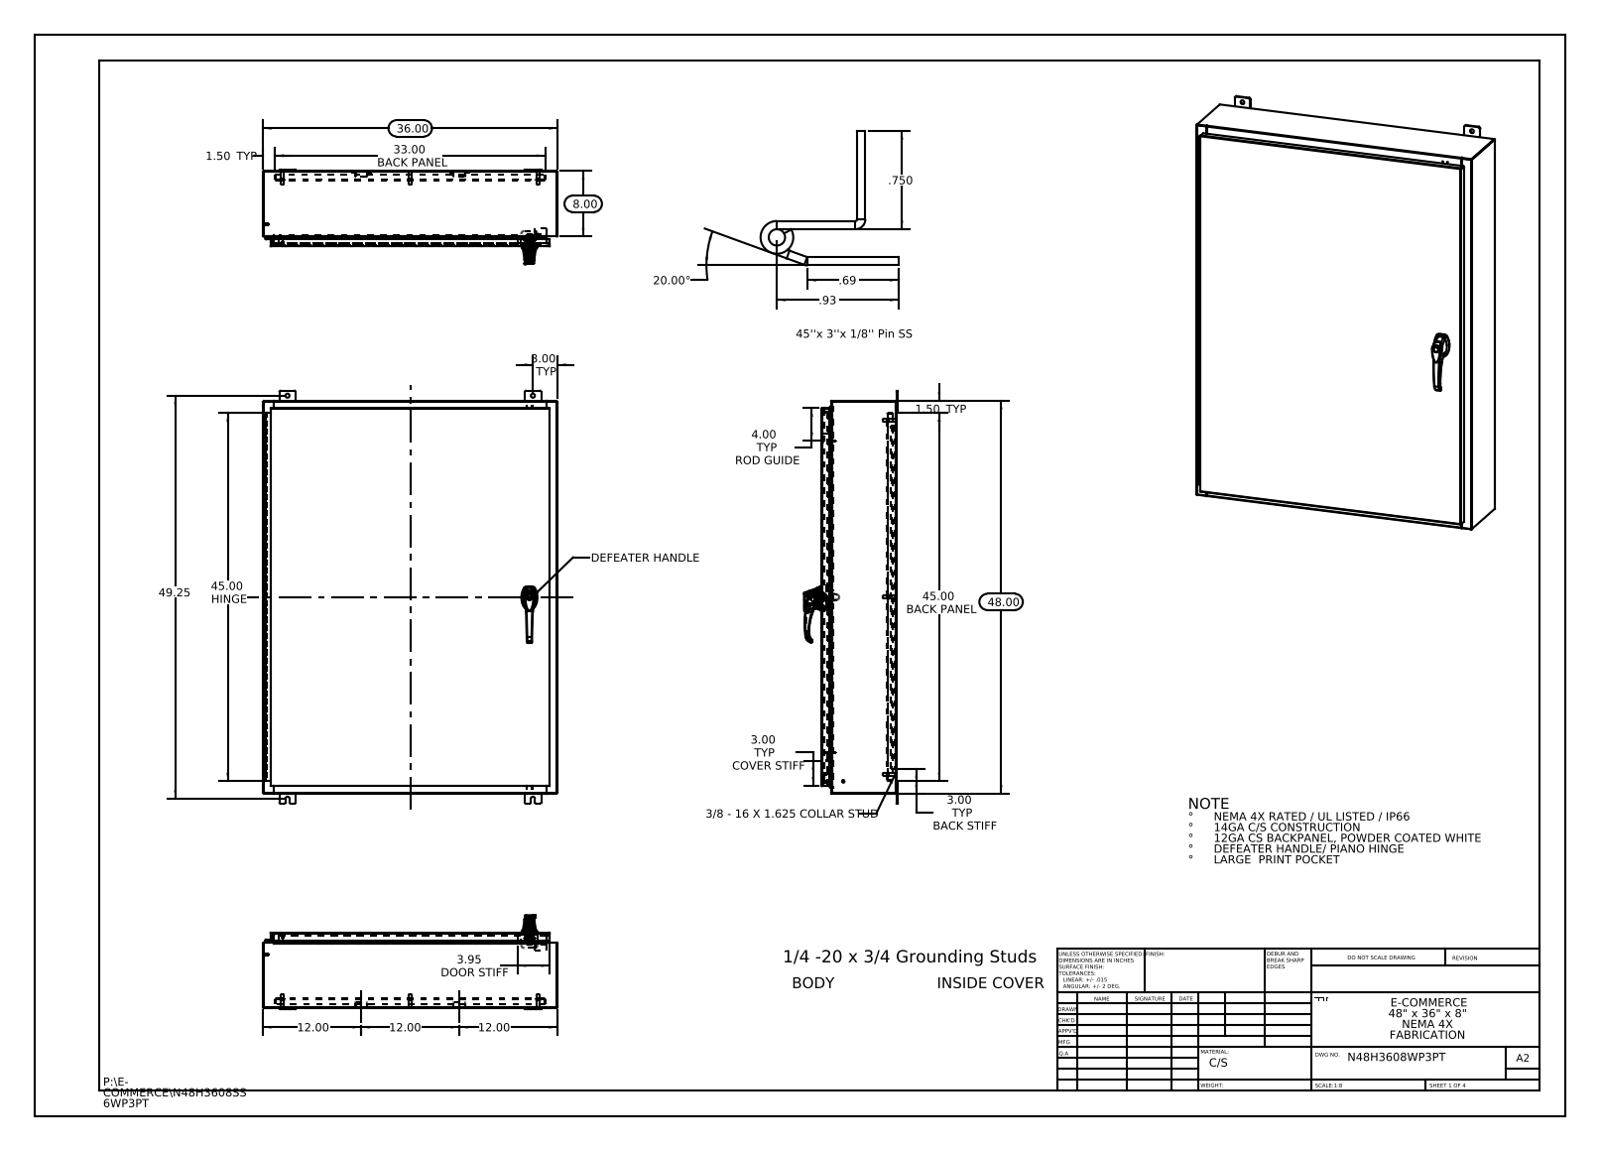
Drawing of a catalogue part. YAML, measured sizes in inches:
part_name: "N48H3608SS6WP3PT Bottom; 26161102; N48H3608SS6WP3PT Defeater Handle - 3 - 2500-51 ZN; NMP-SS-RODGUIDES (+8 more)"
step_written_by: "SolidWorks 2013 (CONFIG_CONTROL_DESIGN)"
units: inches
bodies: {solids: 51, faces: 3400, planar: 1309, cylindrical: 1305, other: 786}
overall_size: [50.5, 36, 11.495]
volume: 606.1
surface_area: 14968
round_holes:
  - {diameter: 0.5, count: 12}
  - {diameter: 0.25, count: 10}
  - {diameter: 0.138, count: 3}
  - {diameter: 0.161, count: 3}
  - {diameter: 0.079, count: 2}
  - {diameter: 0.203, count: 2}
  - {diameter: 0.313, count: 2}
  - {diameter: 0.437, count: 2}
  - {diameter: 0.125, count: 1}
  - {diameter: 0.125, count: 1}
  - {diameter: 0.197, count: 1}
  - {diameter: 0.276, count: 1}
round_bosses_or_shafts:
  - {diameter: 0.157, count: 10}
  - {diameter: 0.14, count: 10}
  - {diameter: 0.625, count: 8}
  - {diameter: 0.375, count: 8}
  - {diameter: 0.33, count: 8}
  - {diameter: 0.315, count: 3}
  - {diameter: 0.236, count: 3}
  - {diameter: 1.181, count: 1}
partial_cylinders:
  - {radius: 0.118, count: 37}
  - {radius: 0.013, count: 34}
  - {radius: 0.006, count: 33}
  - {radius: 0.088, count: 28}
  - {radius: 0.19, count: 24}
  - {radius: 0.039, count: 15}
  - {radius: 0.028, count: 12}
  - {radius: 0.008, count: 6}
face_to_face_distances: [0.075, 9.126, 9.051, 9.201, 0.104, 1, 8.126, 1.075, 8.051, 1.179]
hole_center_spacings: [17.357, 19.665, 21.625, 38.003, 45.986, 31.25, 43.25, 0.295]
